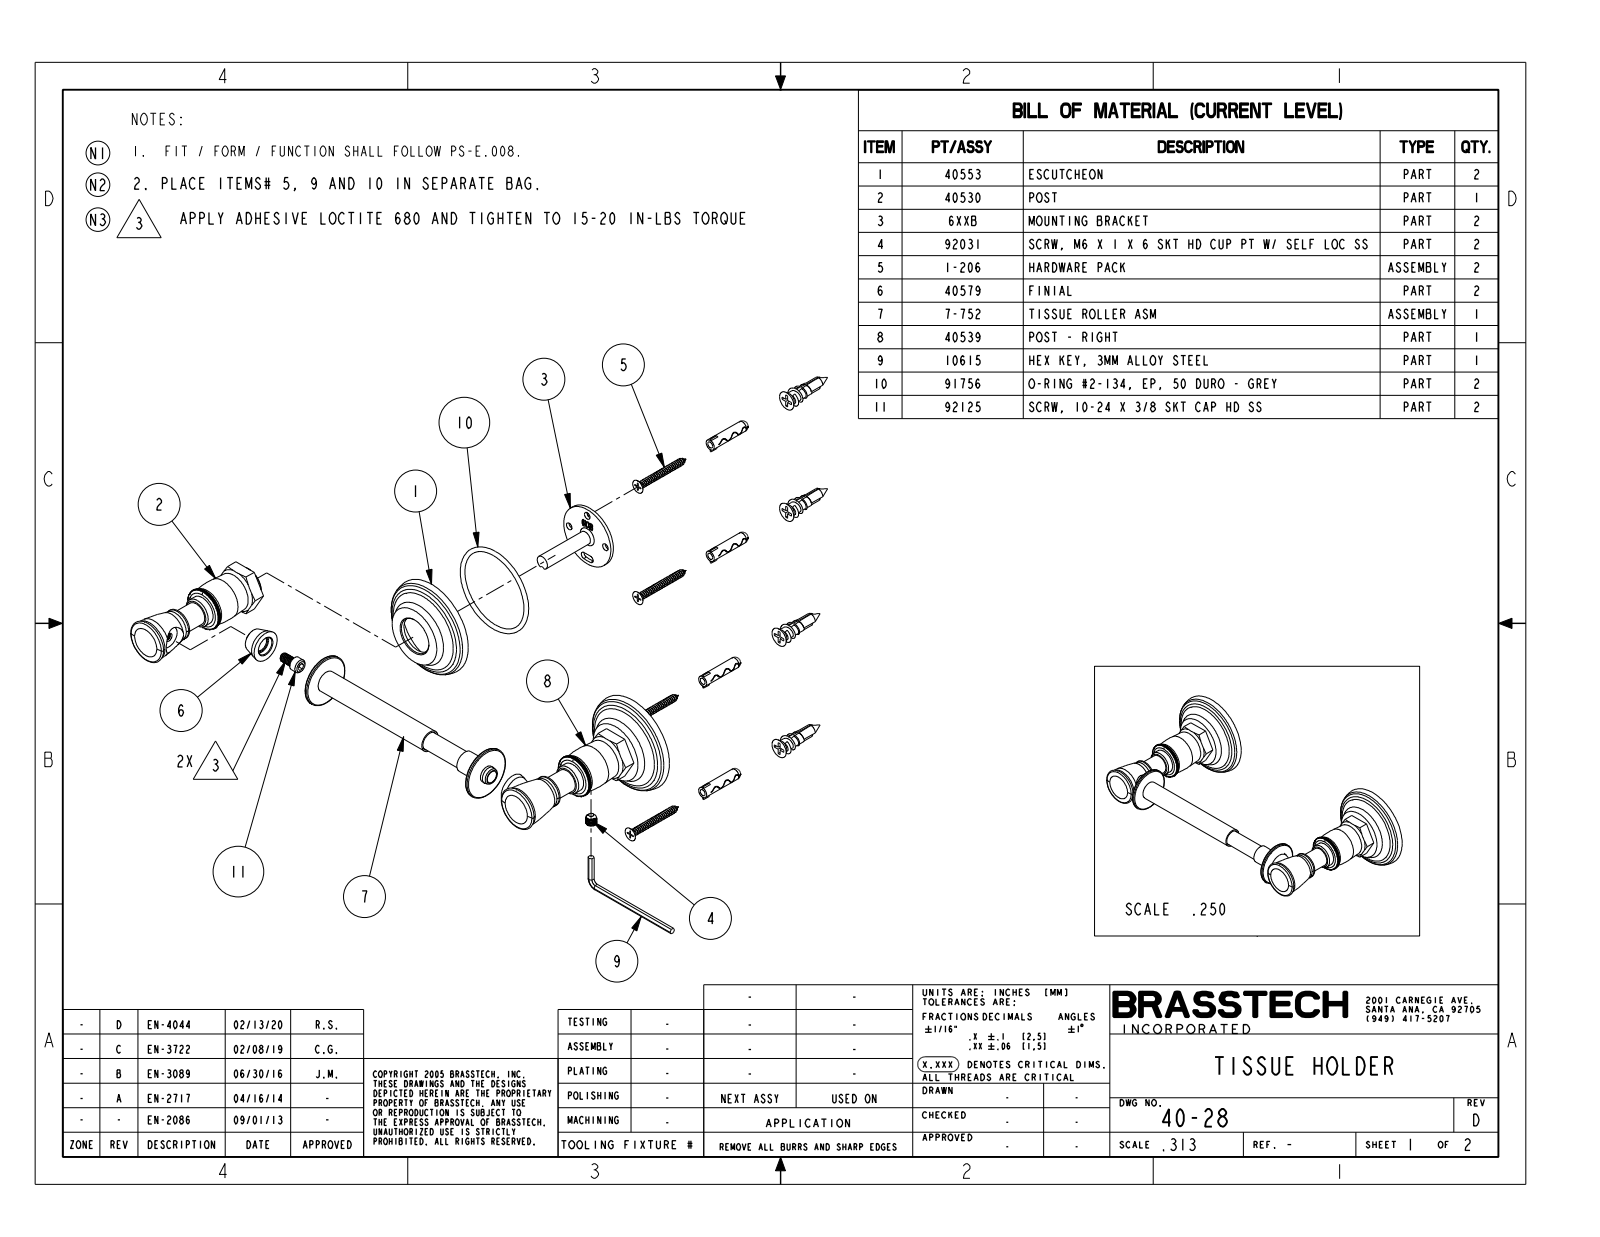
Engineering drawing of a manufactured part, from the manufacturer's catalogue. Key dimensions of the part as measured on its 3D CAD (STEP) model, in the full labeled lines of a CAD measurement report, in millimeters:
Part name (STEP PRODUCT): 40553; 40530; 6XXB; 92031 (+8 more)
STEP written by: PRO/ENGINEER BY PARAMETRIC TECHNOLOGY CORPORATION, 2013150 (CONFIG_CONTROL_DESIGN)
Units: millimetres
Bodies: 16 solids, 1880 faces (1136 planar, 262 cylindrical, 482 other)
Overall size (bounding box): 222.8 × 92.7 × 57.7
Volume: 84 480 mm³ · Surface area: 93 940 mm²
Round holes (diameter × count): ⌀4.3 ×6, ⌀8.1 ×2, ⌀21.6 ×2, ⌀46.5 ×2, ⌀53.6 ×2, ⌀3.8 ×1, ⌀5 ×1, ⌀5 ×1, ⌀5 ×1, ⌀8.4 ×1, ⌀14.9 ×1, ⌀16.3 ×1
Round bosses / shafts (diameter × count): ⌀5.2 ×8, ⌀48.3 ×2, ⌀37.1 ×2, ⌀21 ×2, ⌀17 ×2, ⌀13.5 ×2, ⌀8 ×2, ⌀6 ×2
Partial cylindrical surfaces — rounded edges, fillets, slot ends (radius × count): R2.2 ×4, R2.6 ×4, R30.8 ×2, R45.4 ×2, R4 ×1
Main face-to-face distances: 2, 13.6, 11.5, 2.2, 11.4, 2.5, 25.1, 11, 9, 8.9
Hole centre spacings: 14.3, 165.1, 20.2, 28.6, 150.8, 151.5, 165.7, 179.4
